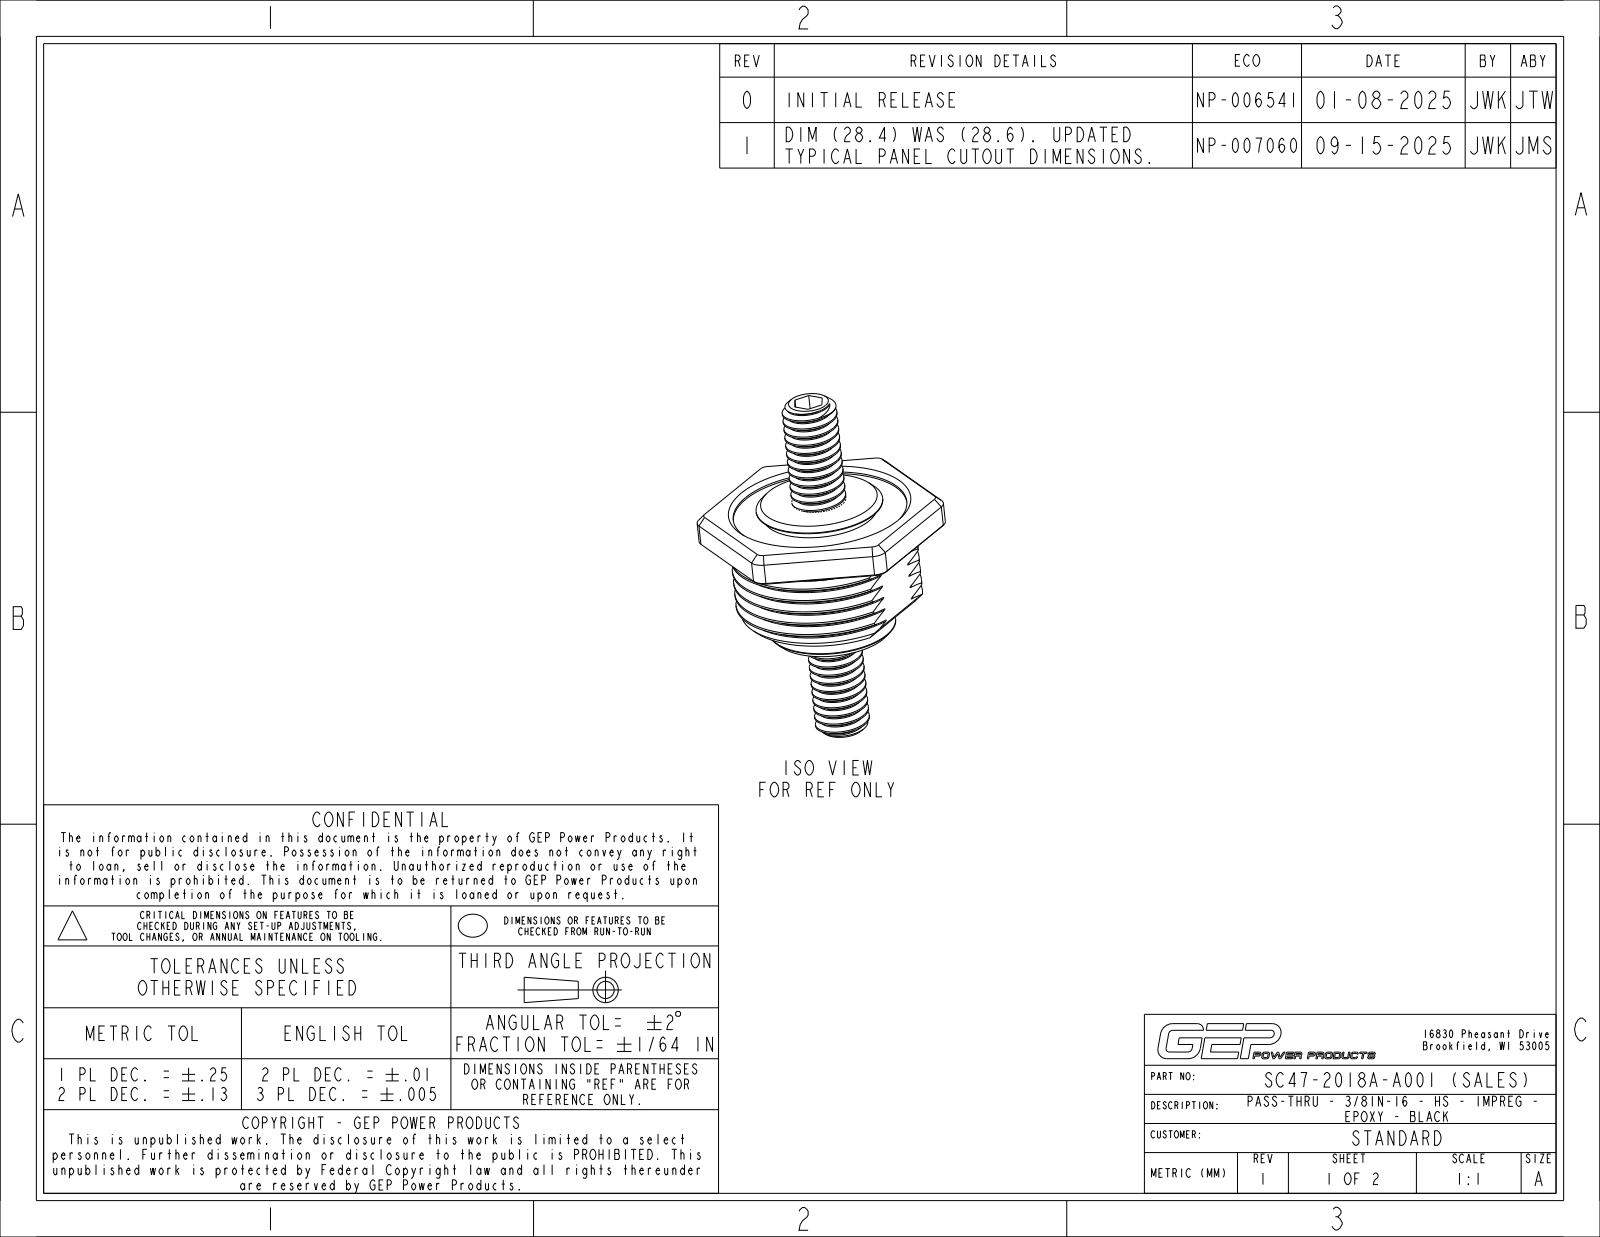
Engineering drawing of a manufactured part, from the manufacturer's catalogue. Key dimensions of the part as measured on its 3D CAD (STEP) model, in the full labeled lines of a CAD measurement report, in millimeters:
Part name (STEP PRODUCT): C07-1001_NCF; PC40-2004A-B001_MOLD_NCF; PC40-2004A-B001_NCF_ASM; PC05-2015A-A000_NCF (+6 more)
STEP written by: CREO PARAMETRIC BY PTC INC, 2024014 (CONFIG_CONTROL_DESIGN)
Units: millimetres
Bodies: 5 solids, 603 faces (289 planar, 149 cylindrical, 165 other)
Overall size (bounding box): 63.5 × 43.2 × 38.1
Volume: 20 750 mm³ · Surface area: 14 700 mm²
Round holes (diameter × count): ⌀8 ×1, ⌀18.2 ×1, ⌀22.2 ×1, ⌀30.5 ×1
Round bosses / shafts (diameter × count): ⌀22.2 ×1, ⌀18.2 ×1, ⌀9.5 ×1
Partial cylindrical surfaces — rounded edges, fillets, slot ends (radius × count): R2.5 ×6, R0.8 ×2, R16.4 ×1
Main face-to-face distances: 12.8, 4.3, 21.1, 12.8, 6.4, 2, 19.1, 1.3, 25.4, 5.1
